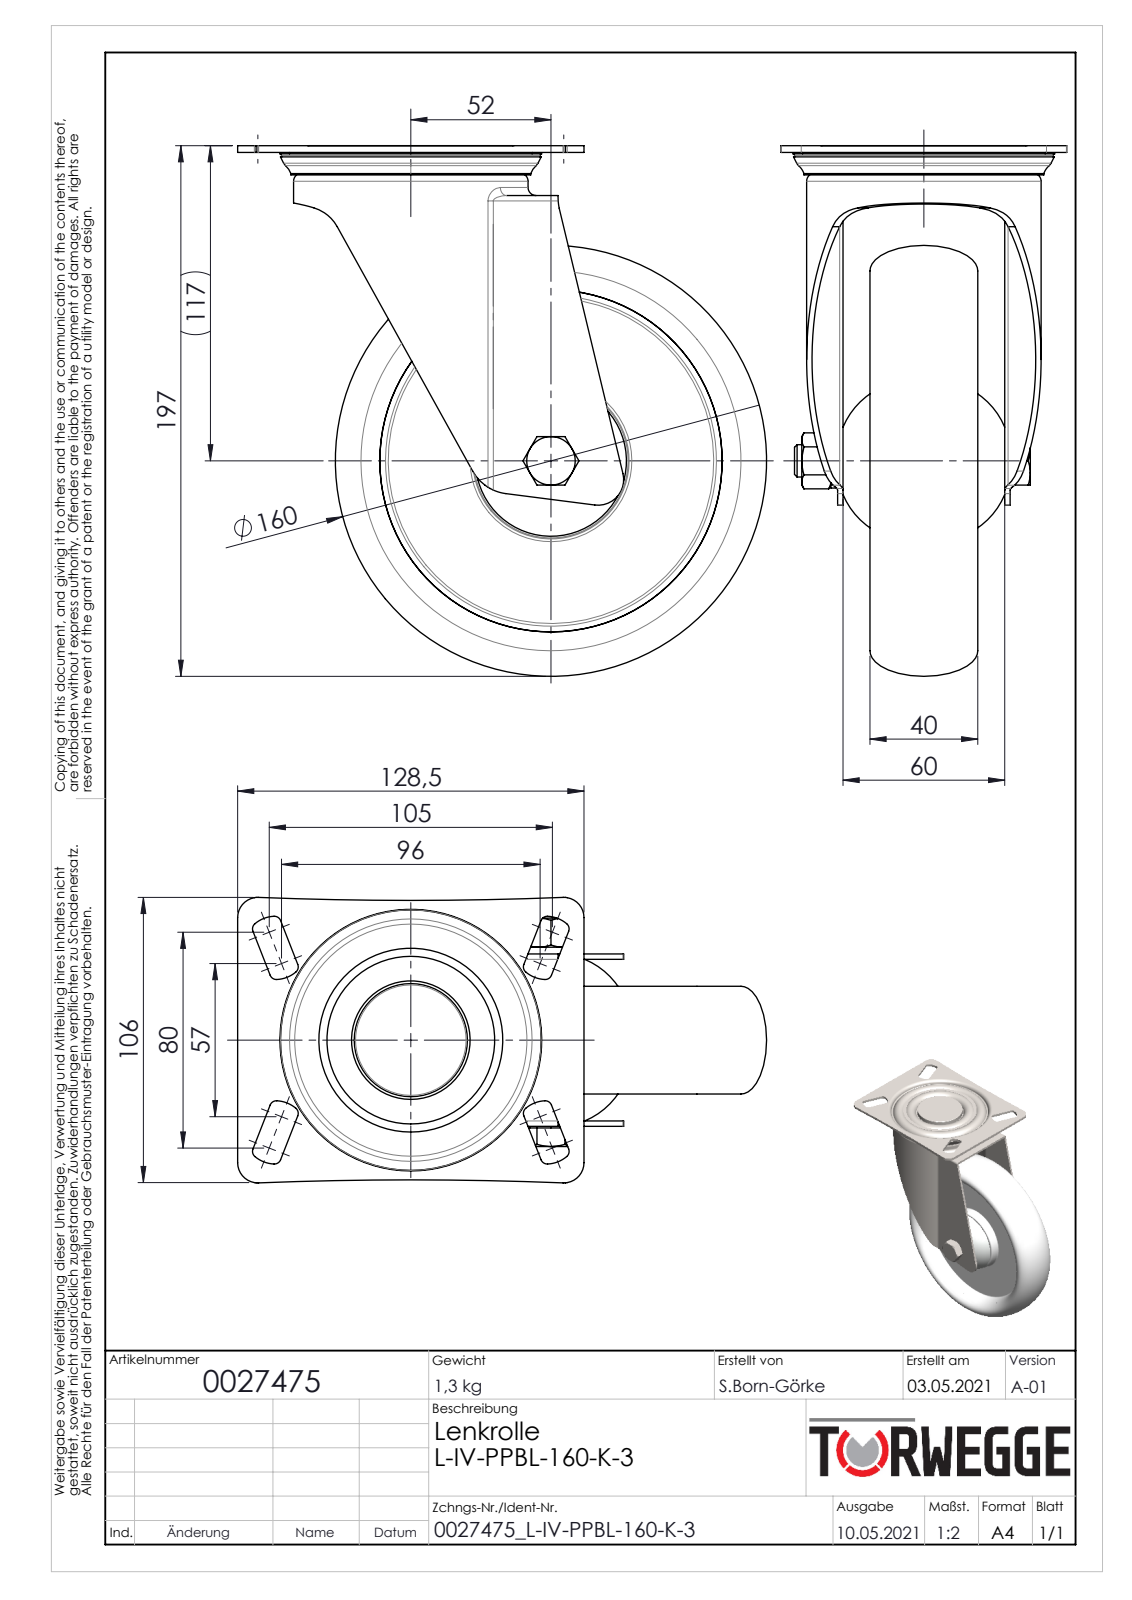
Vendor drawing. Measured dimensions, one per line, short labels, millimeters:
name: 0027475
written by: SolidWorks 2020 (AUTOMOTIVE_DESIGN)
unit: mm
bodies: 0 solids, 441 faces (94 planar, 148 cylindrical, 199 other)
size: 197.02 × 196.25 × 106
holes: 1× ⌀10.2, 1× ⌀12, 1× ⌀12.2, 1× ⌀38, 1× ⌀39, 1× ⌀42, 1× ⌀45, 1× ⌀47, 1× ⌀54, 1× ⌀55.5, 1× ⌀66, 1× ⌀83
bosses: 1× ⌀89, 1× ⌀87, 1× ⌀70, 1× ⌀50.5, 1× ⌀41, 1× ⌀34, 1× ⌀20.2, 1× ⌀20
rounds: 40× R2.5, 4× R7.5, 4× R11.75, 2× R2, 2× R3, 2× R5, 2× R1424.42, 1× R9.5
face distances: 2, 9.5, 34.75, 25.25, 62, 27.25, 36.75, 2.5, 60, 64
